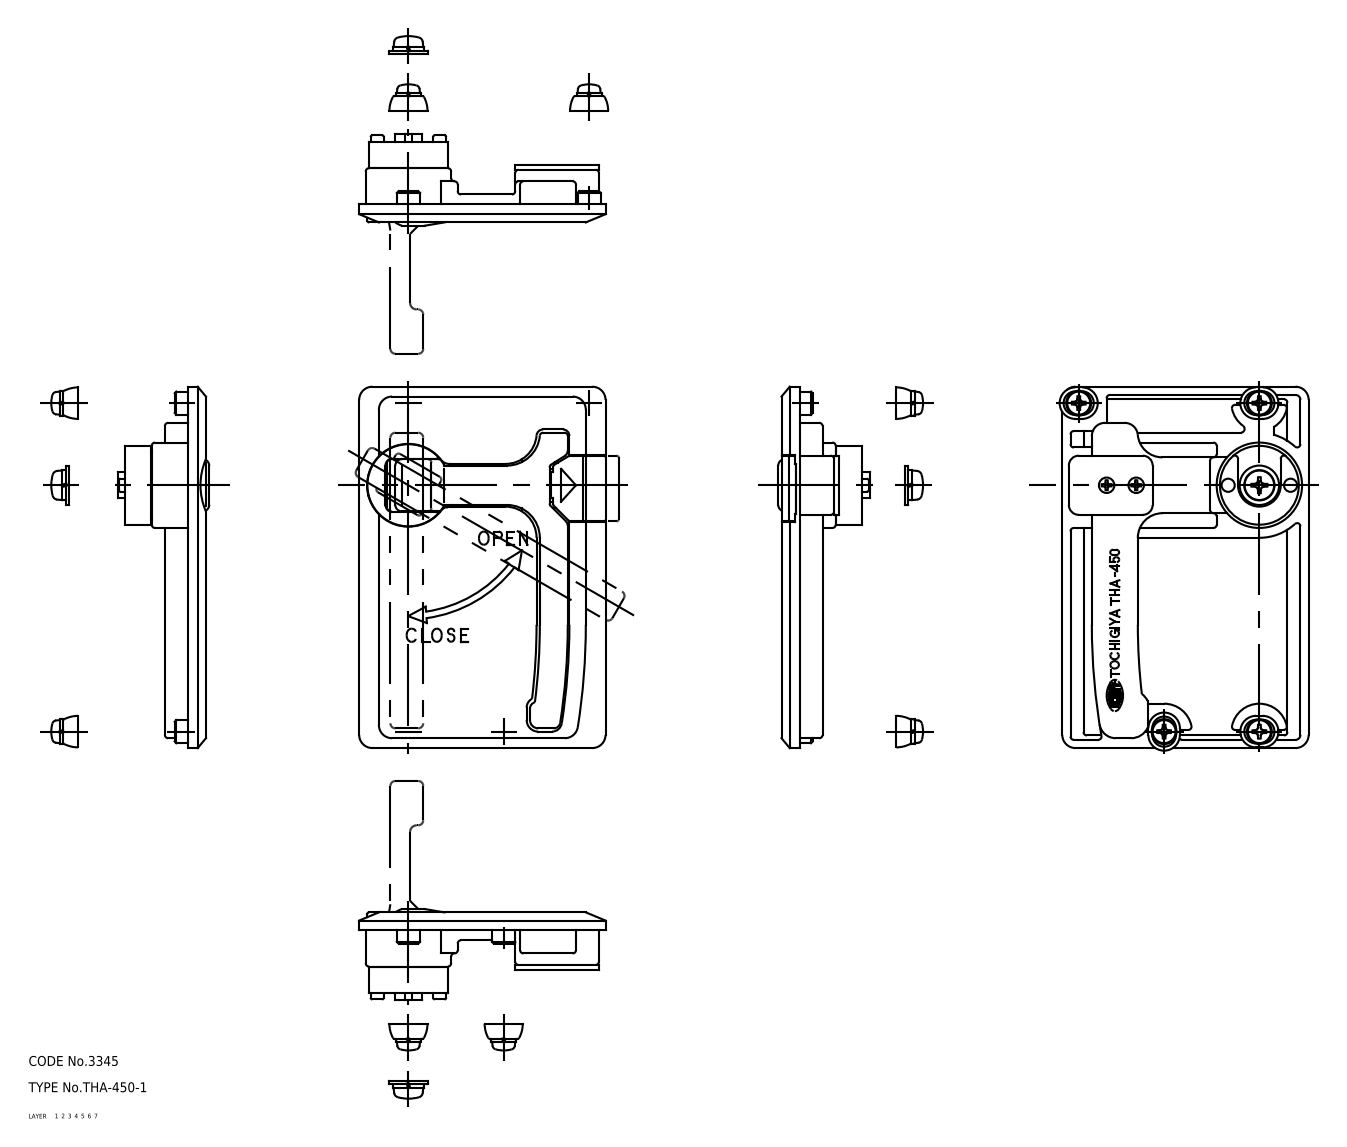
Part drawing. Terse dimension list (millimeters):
name: bracket; screw_A; screw_B; shaft (+6 more)
written by: CADfix (AUTOMOTIVE_DESIGN)
unit: mm
bodies: 15 solids, 691 faces (0 planar, 0 cylindrical, 691 other)
size: 110.8 × 75.8 × 33.16
volume: 48 090 mm³; area: 40 590 mm²
